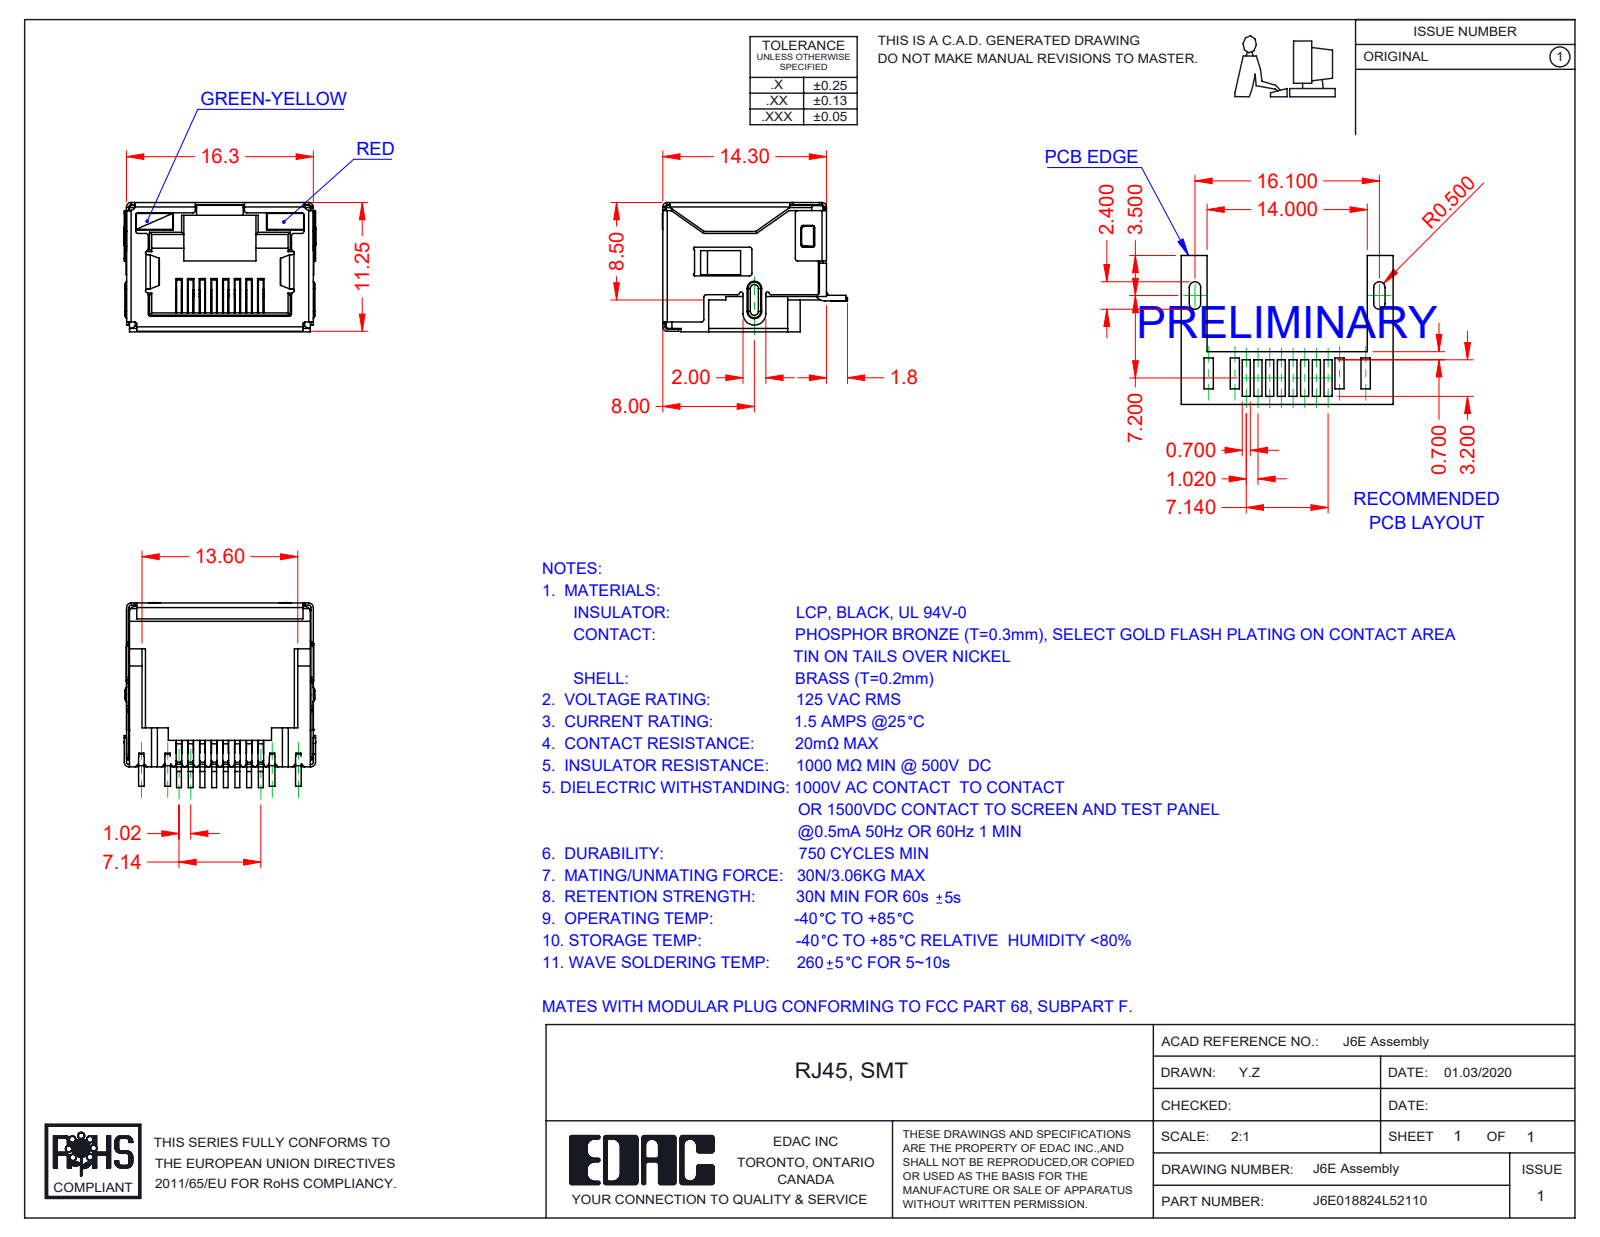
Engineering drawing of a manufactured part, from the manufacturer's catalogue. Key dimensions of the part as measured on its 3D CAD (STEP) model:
Part name (STEP PRODUCT): J6E018824L52110; 6E Shield_LED; 6E Contacts; 6E LED LH_5-Green-Yellow (+2 more)
STEP written by: SolidWorks 2016 (CONFIG_CONTROL_DESIGN)
Units: millimetres
Bodies: 12 solids, 1498 faces (1099 planar, 349 cylindrical, 50 other)
Overall size (bounding box): 16.75 × 16.15 × 11.3
Volume: 1 109 mm³ · Surface area: 4 045 mm²
Partial cylindrical surfaces — rounded edges, fillets, slot ends (radius × count): R0.2 ×82, R0.25 ×17, R0.4 ×13, R0.5 ×13, R0.1 ×10, R0.15 ×7, R0.3 ×4, R1 ×3
Main face-to-face distances: 11.05, 16.05, 16.1, 15.85, 11.1, 11.3, 2.4, 0.7, 9.85, 0.49
